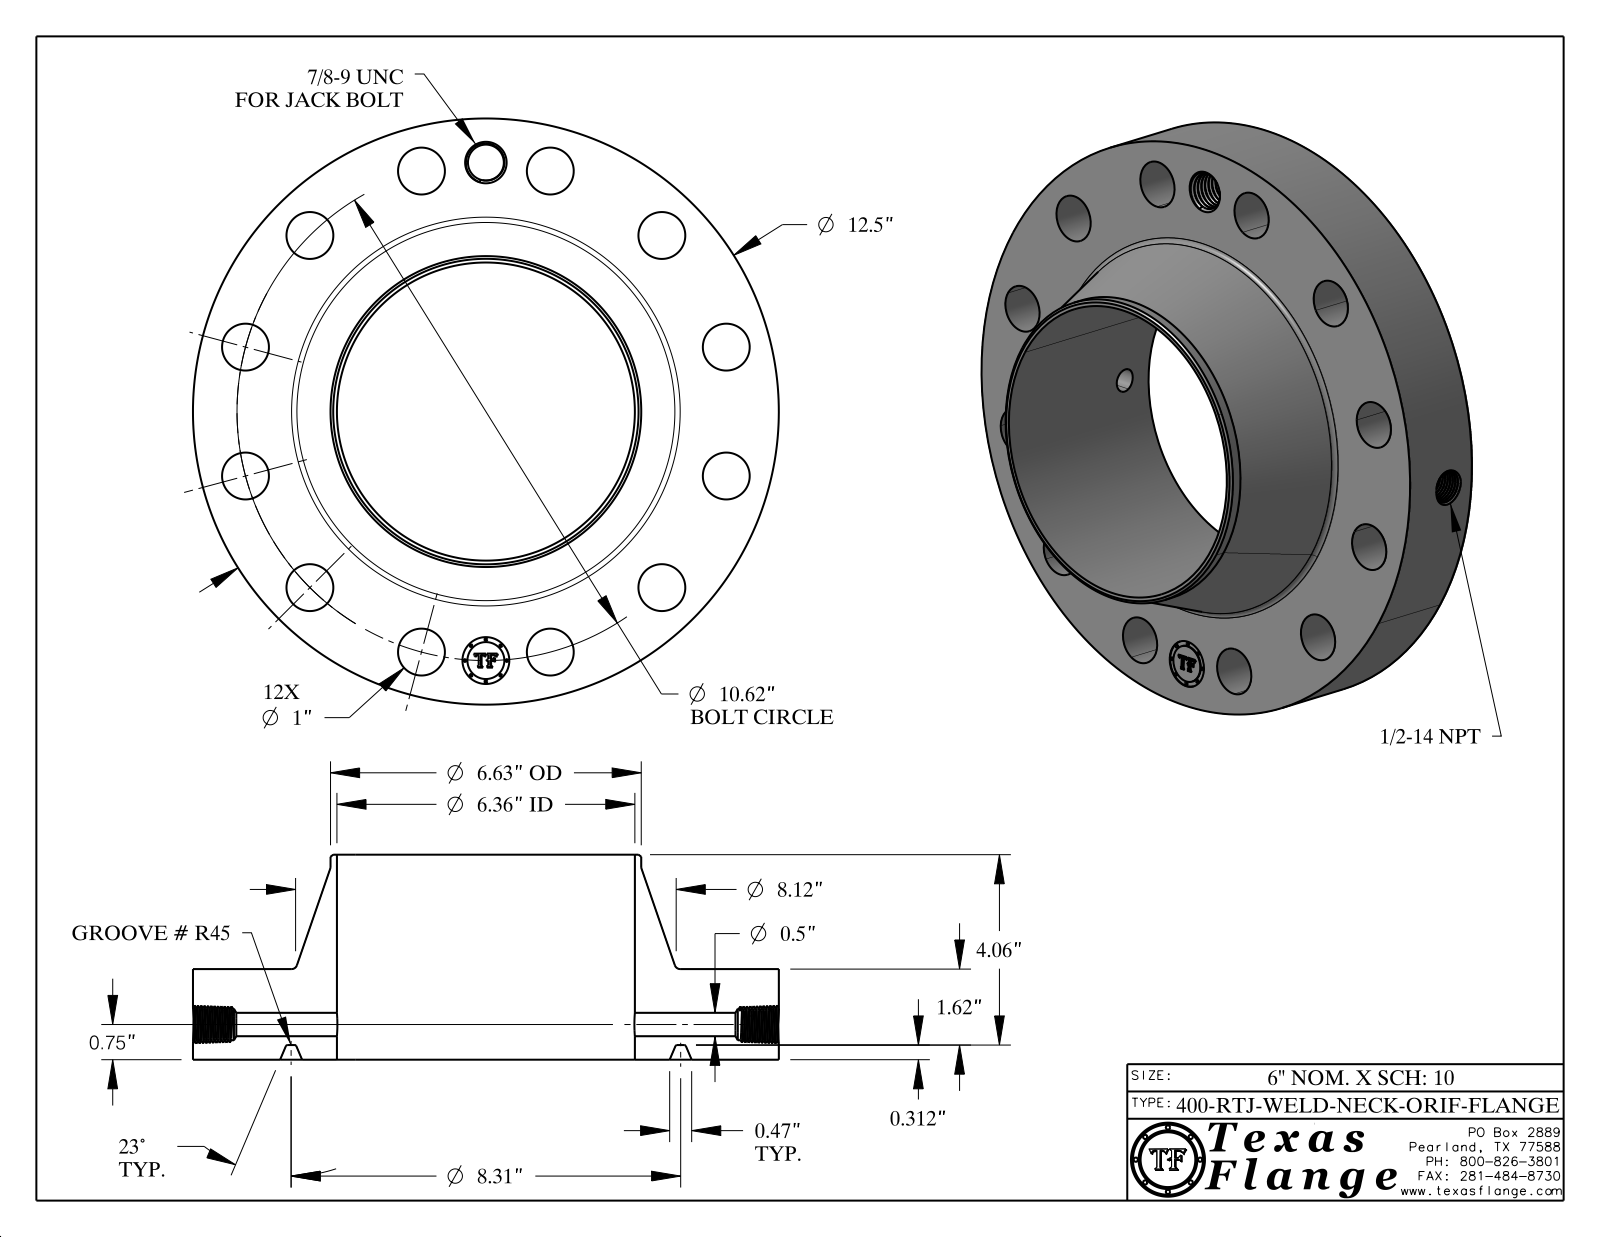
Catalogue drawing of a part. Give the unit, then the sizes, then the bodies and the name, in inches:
Units: inches
Overall size (bounding box): 12.5 × 12.5 × 4.372
Round holes (diameter × count): ⌀1 ×13, ⌀0.5 ×1, ⌀0.672 ×1, ⌀0.766 ×1, ⌀6.357 ×1
Round bosses / shafts (diameter × count): ⌀0.061 ×8, ⌀12.5 ×1, ⌀6.63 ×1, ⌀0.788 ×1
Main face-to-face distances: 1.932, 0.312, 1.62, 4.372, 4.06, 2.44, 0.015, 1.917, 1.605, 2.455
Hole centre spacings: 5.31, 7.509, 9.197, 10.258, 5.31, 2.748, 10.62, 1.386
Volume: 177 in³ · Surface area: 469 in²
Bodies: 1 solid, 796 faces (370 planar, 104 cylindrical, 322 other)
Part name (STEP PRODUCT): 400-RTJ-WELD-NECK
STEP written by: CATIA V5 STEP AP214 (AUTOMOTIVE_DESIGN)
